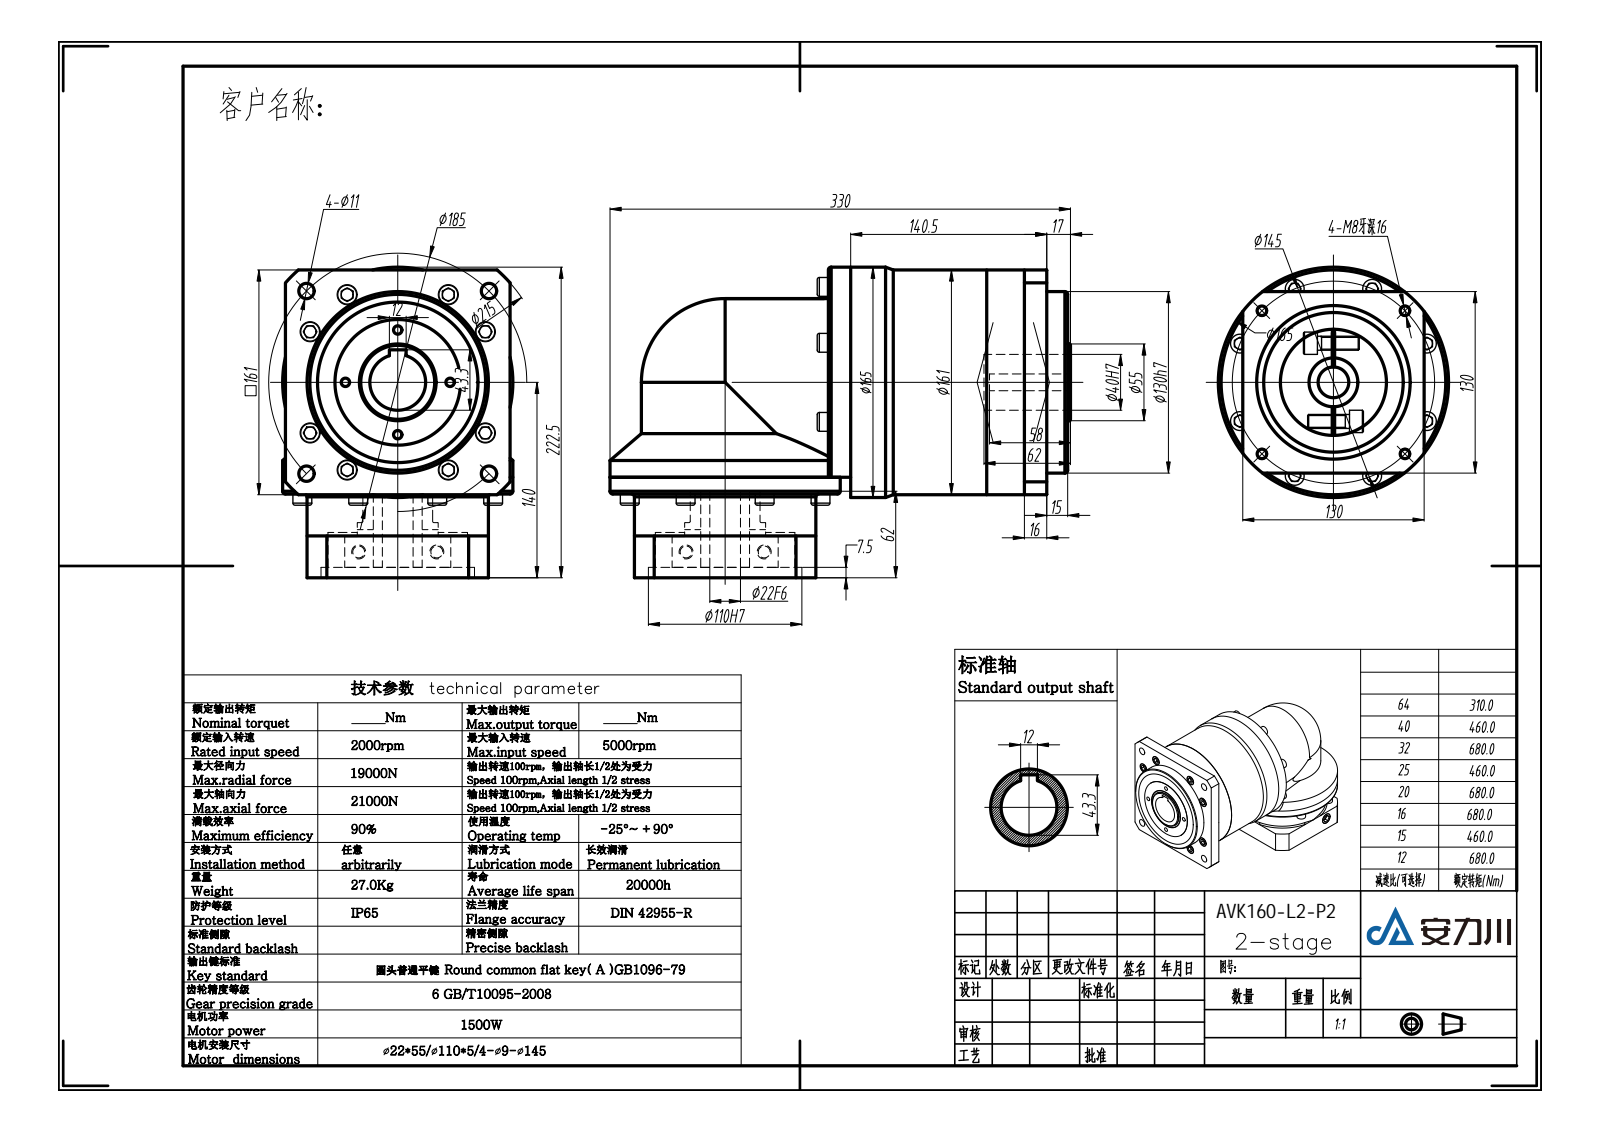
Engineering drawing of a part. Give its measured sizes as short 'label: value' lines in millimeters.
name: VGZK160双级模型（22-55 110-5 4-9-145） 轴套; VGK160双级输出部分; VGZE160转角部分（22-55 110-5 4-9-145） 轴套
written by: SolidWorks 2016 (AUTOMOTIVE_DESIGN)
unit: mm
bodies: 5 solids, 459 faces (259 planar, 149 cylindrical, 51 other)
size: 330 × 222.5 × 165
volume: 6 034 000 mm³; area: 425 227 mm²
holes: 8× ⌀14, 4× ⌀6, 4× ⌀6.8, 4× ⌀11, 2× ⌀16, 1× ⌀22, 1× ⌀35, 1× ⌀40, 1× ⌀61, 1× ⌀90, 1× ⌀100, 1× ⌀110
bosses: 20× ⌀13, 2× ⌀165, 2× ⌀130, 2× ⌀15.6, 1× ⌀161, 1× ⌀115, 1× ⌀90, 1× ⌀76
rounds: 1× R57.5, 1× R107.5
face distances: 97.5, 140.5, 16, 43, 60, 30, 72, 156.5, 29.5, 113.5
hole spacings: 72.5, 131.46, 102.53, 29.27, 29.28, 37.5, 44.19, 44.2
